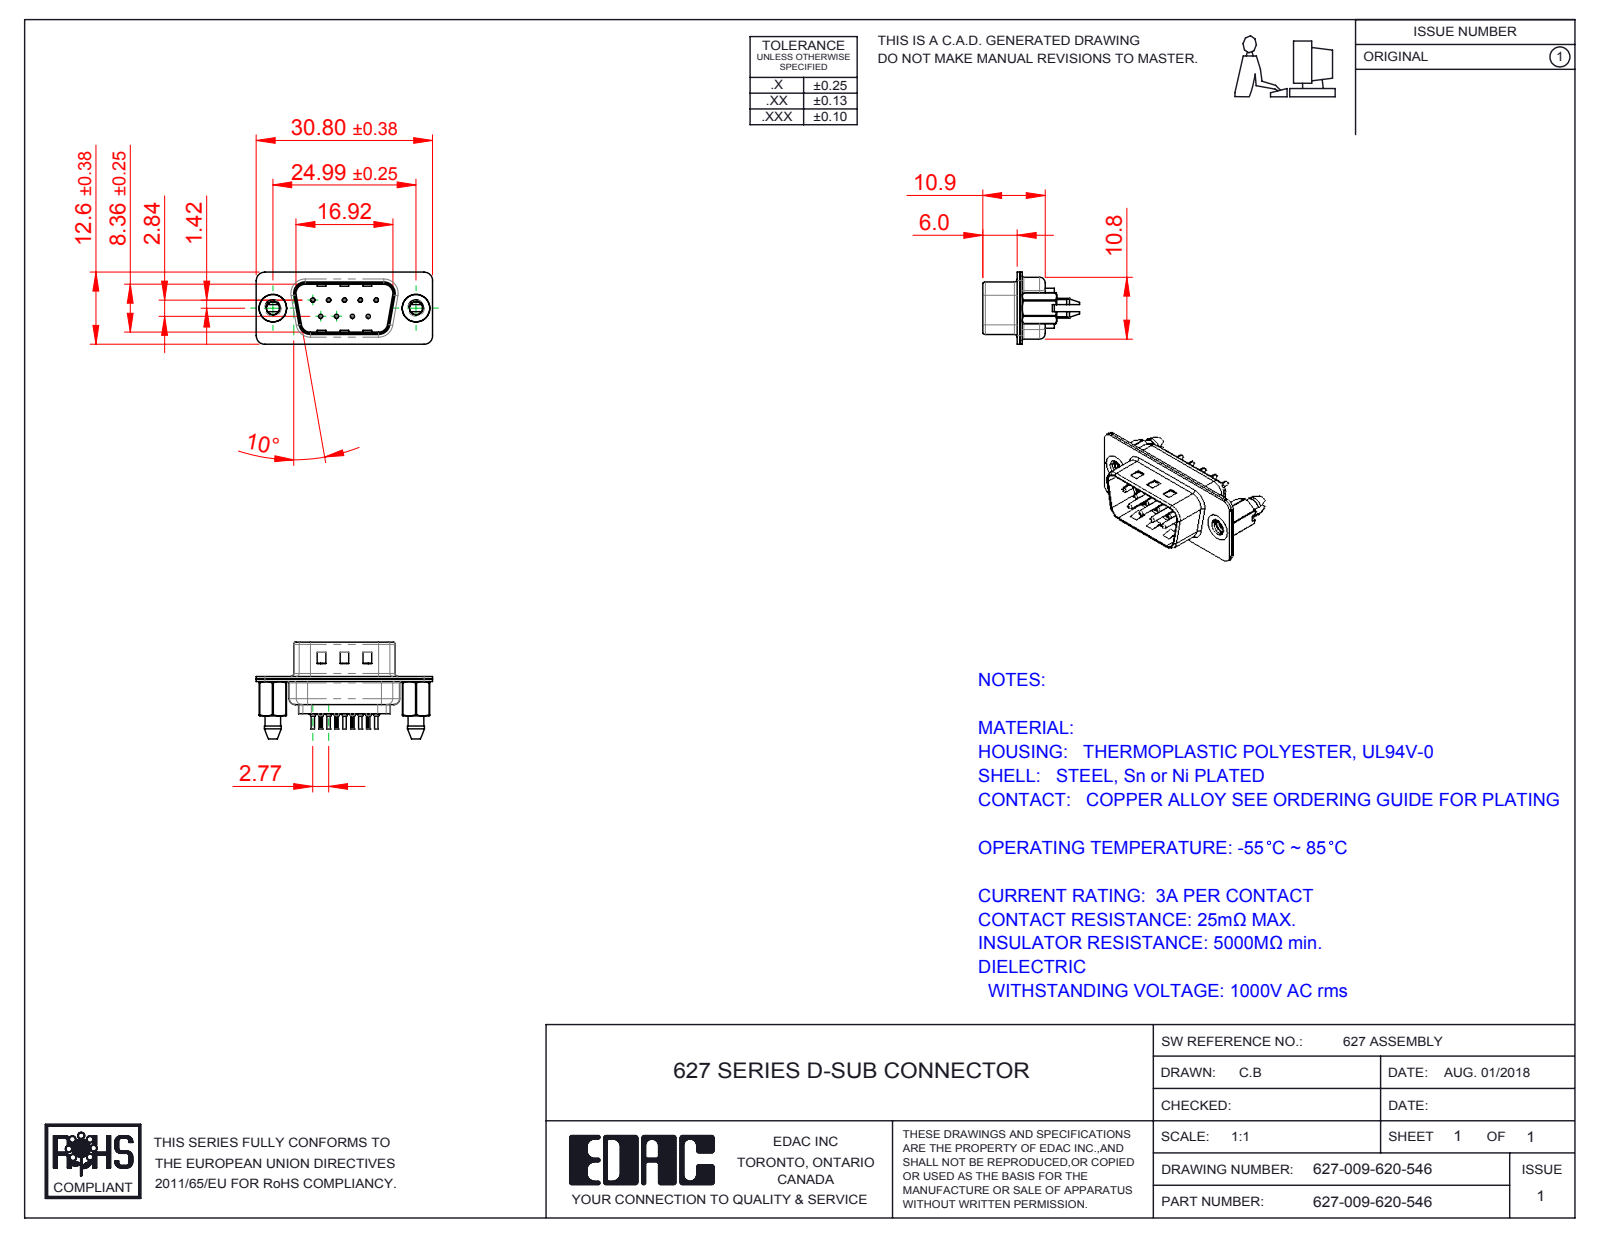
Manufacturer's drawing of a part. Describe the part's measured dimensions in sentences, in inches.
The part is named "627 4-40 Threaded Boardlock_LP; 627 Contact Row 1_20L; 627-009-620-546; 627 Shell Front_09 Contacts (+3 more)". Its 3-D file was written by "SolidWorks 2016 (CONFIG_CONTROL_DESIGN)". It is 14 solids with 1260 faces: 355 planar, 494 cylindrical and 411 other. Overall it measures 1.213 by 0.665 by 0.496 inches. Its volume is 0.087 cubic inches and its surface area 6.465 square inches. Round holes: 9 of diameter 0.008, 9 of diameter 0.014, 9 of diameter 0.043, 9 of diameter 0.063, 2 of diameter 0.089, 2 of diameter 0.157, 2 of diameter 0.189. Round bosses or shafts: 9 of diameter 0.079, 9 of diameter 0.059, 9 of diameter 0.03, 9 of diameter 0.024, 2 of diameter 0.193. Partial cylindrical surfaces (rounded edges, fillets, slot ends): 20 of radius 0.059, 18 of radius 0.004, 12 of radius 0.079, 10 of radius 0.063, 8 of radius 0.02, 4 of radius 0.01, 4 of radius 0.024, 4 of radius 0.026. The main face-to-face distances are 0.018, 0.016, 0.035, 0.032, 0.377, 0.055, 0.345, 0.256, 0.02, 0.059. The hole center spacings are 0.124, 0.109, 0.218, 0.198, 0.198, 0.327, 0.294, 0.295.
